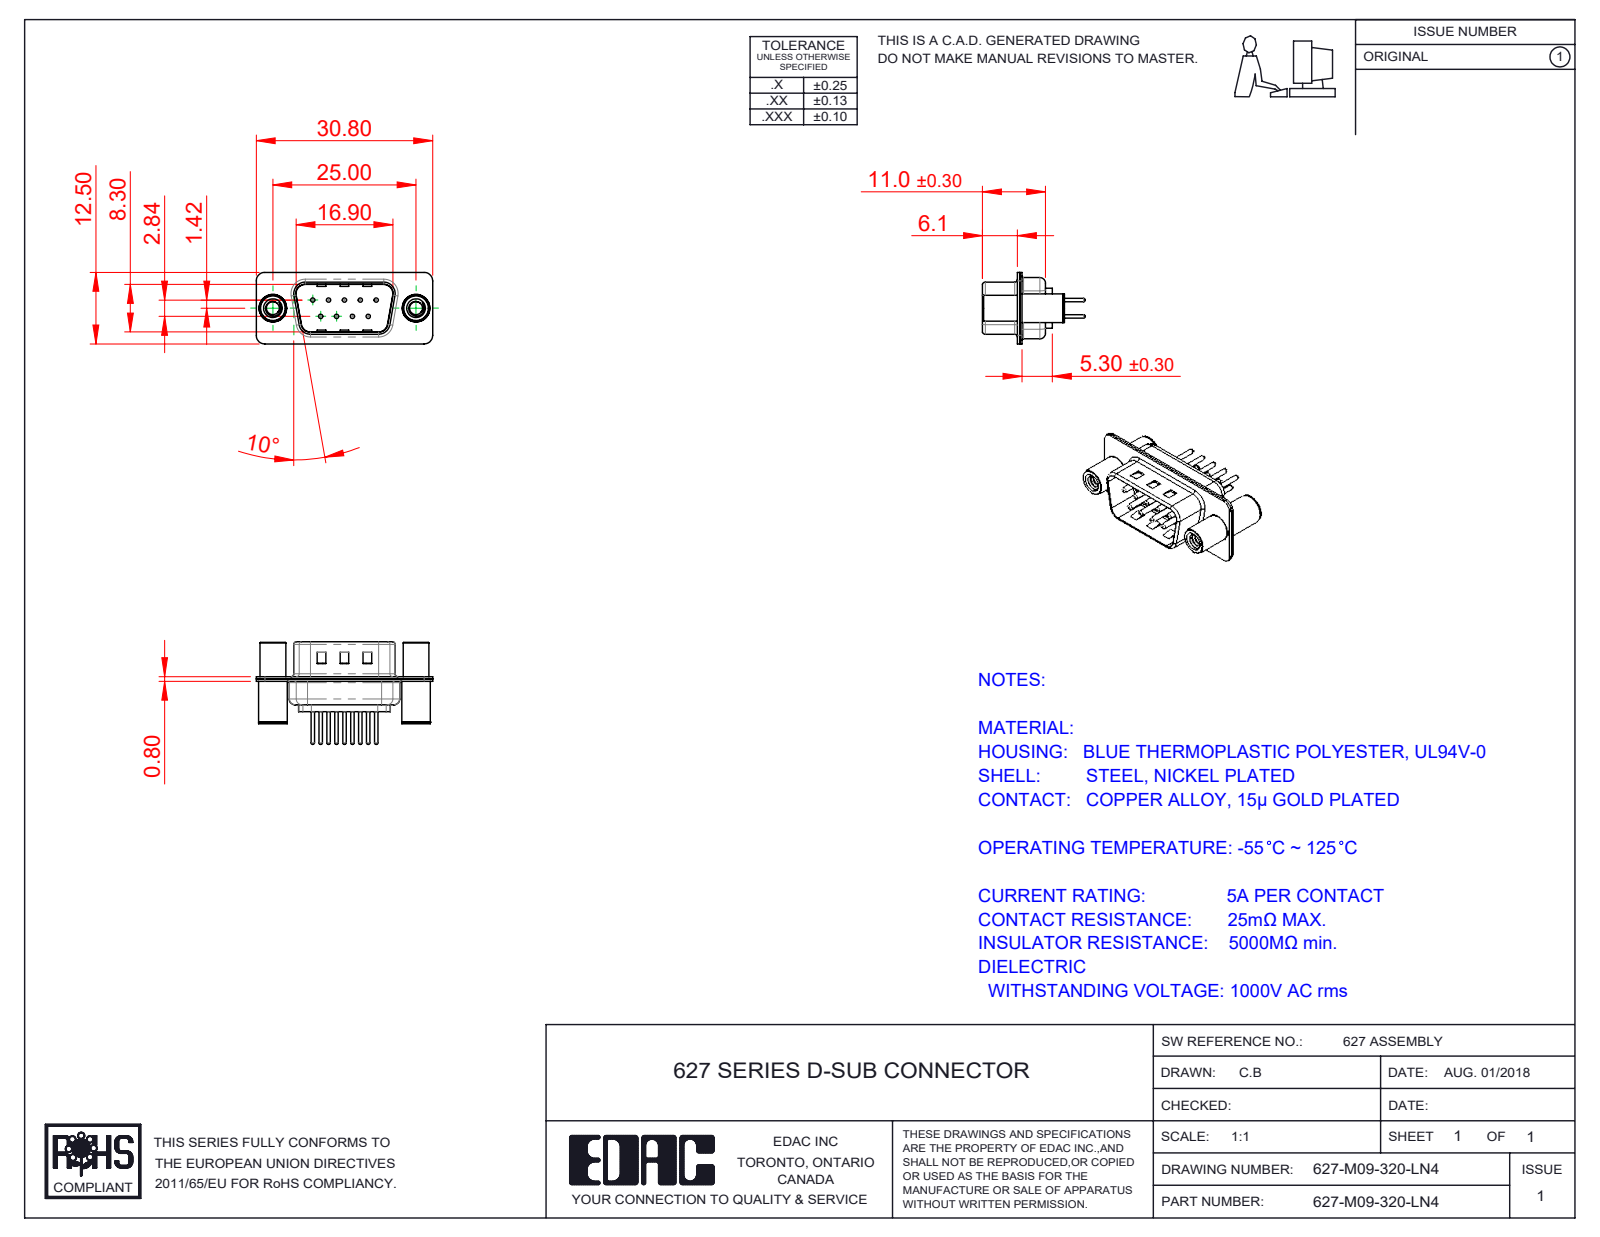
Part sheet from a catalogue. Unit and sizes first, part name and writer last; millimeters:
Units: millimetres
Overall size (bounding box): 30.8 × 17.9 × 12.5
Round holes (diameter × count): ⌀0.75 ×9, ⌀1.6 ×9, ⌀2 ×9, ⌀2.26 ×2, ⌀3.26 ×2, ⌀4 ×2, ⌀4.8 ×2
Round bosses / shafts (diameter × count): ⌀1.5 ×9, ⌀0.6 ×9, ⌀5 ×2, ⌀4.9 ×2, ⌀4.5 ×2
Partial cylindrical surfaces — rounded edges, fillets, slot ends (radius × count): R1.5 ×16, R2 ×12, R0.5 ×8, R1.6 ×8, R0.25 ×4, R0.6 ×4, R0.65 ×4, R0.9 ×4
Main face-to-face distances: 0.4, 0.8, 9.5, 9.1, 8.7, 0.65, 9.9, 1.2, 5.3, 6.1
Hole centre spacings: 3.16, 2.77, 5.54, 5.03, 5.04, 8.31, 7.1, 7.48
Volume: 1 597 mm³ · Surface area: 4 103 mm²
Bodies: 14 solids, 723 faces (176 planar, 307 cylindrical, 240 other)
Part name (STEP PRODUCT): 627M Shell Rear_09 Contacts; 627M Shell Front_09 Contacts; 627M 4-40 Threaded Standoff and Board Spacer; 627M Housing_09 Contacts (+3 more)
STEP written by: SolidWorks 2020 (CONFIG_CONTROL_DESIGN)
